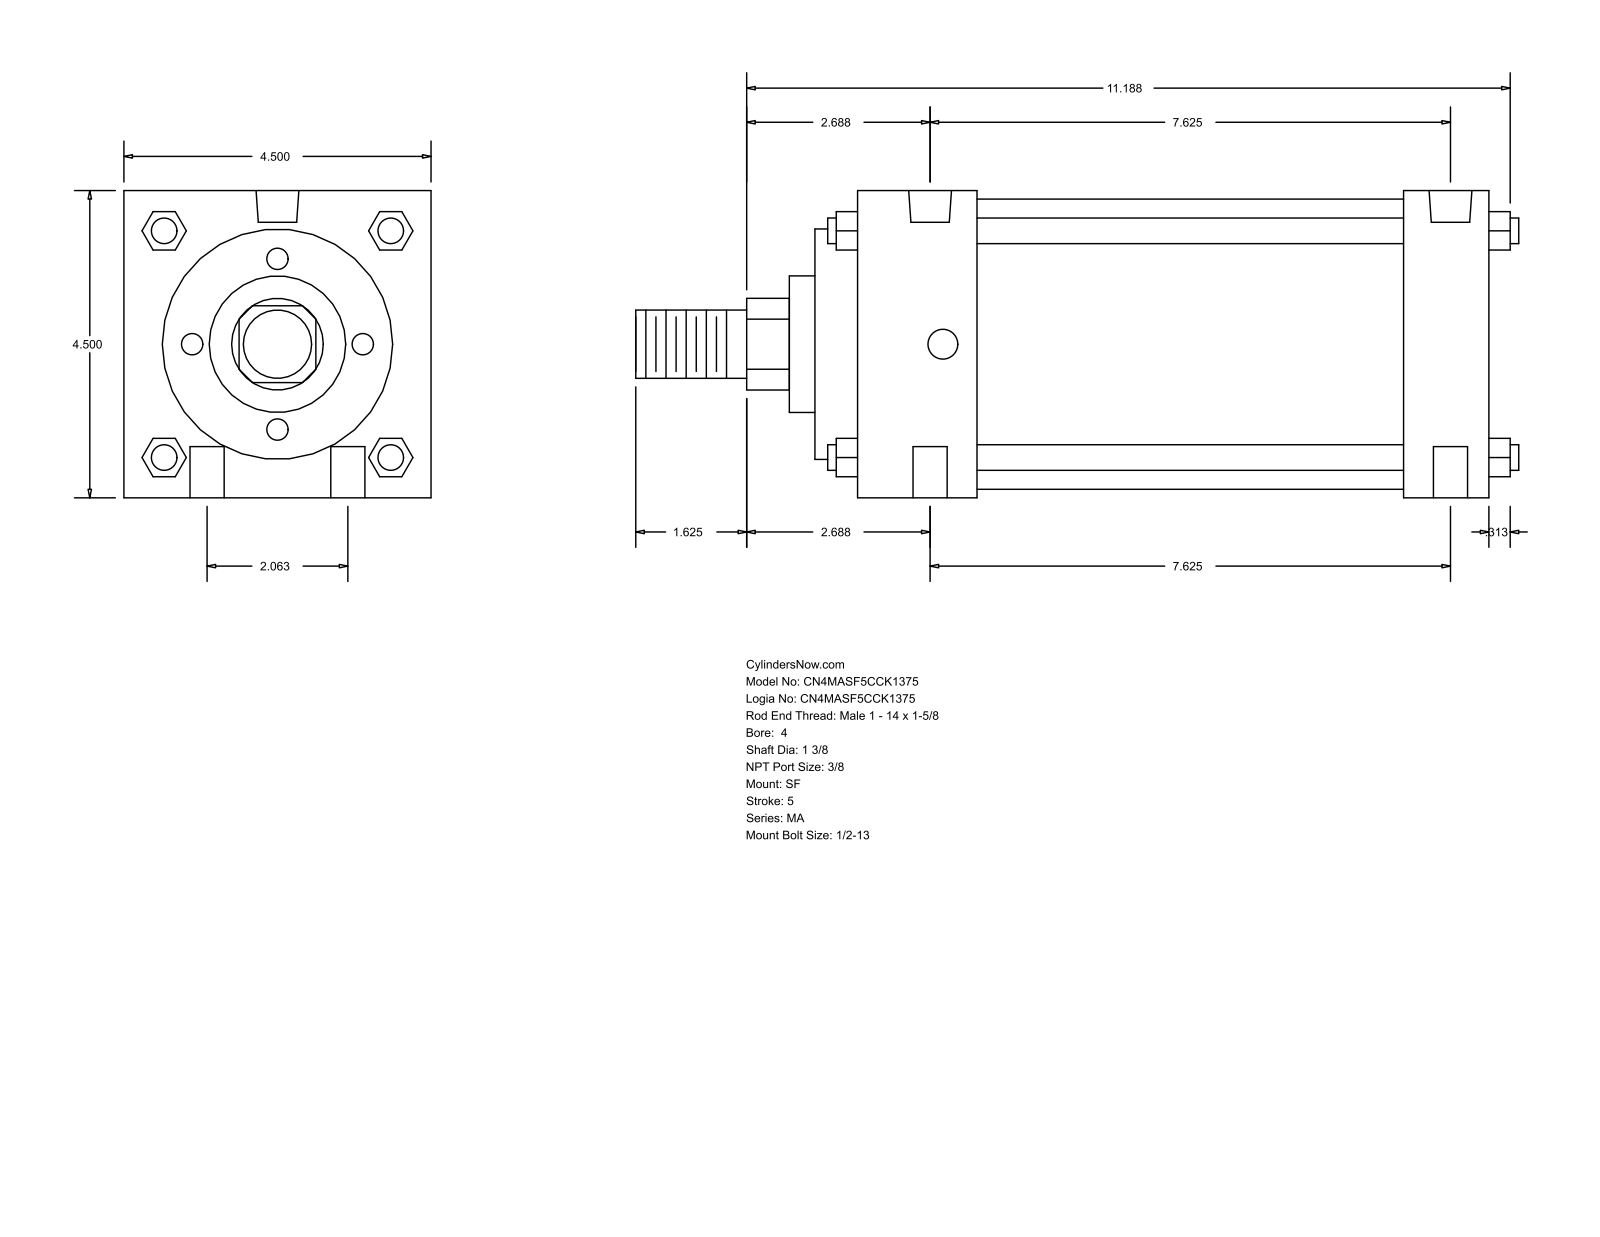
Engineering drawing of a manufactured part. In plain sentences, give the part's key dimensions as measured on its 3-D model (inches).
The part is named "MA_SF__0400_1.375". Its 3-D file was written by "GSSL Pune (CONFIG_CONTROL_DESIGN)". It is 0 solids with 126 faces: 95 planar, 31 cylindrical and 0 other. Overall it measures 12.937 by 4.5 by 4.5 inches. Round holes: 4 of diameter 0.5, 2 of diameter 0.437, 2 of diameter 0.627. Round bosses or shafts: 4 of diameter 0.375, 1 of diameter 4.25, 1 of diameter 3.375, 1 of diameter 2, 1 of diameter 1.375, 1 of diameter 1. Partial cylindrical surfaces (rounded edges, fillets, slot ends): 1 of radius 0.672. The main face-to-face distances are 4.5, 9.25, 0.625, 9.875, 8.625, 8, 1.25, 2.375, 1.75, 6.25. The hole center spacings are 1.031, 7.694, 7.625, 2.062, 7.899, 7.25.
